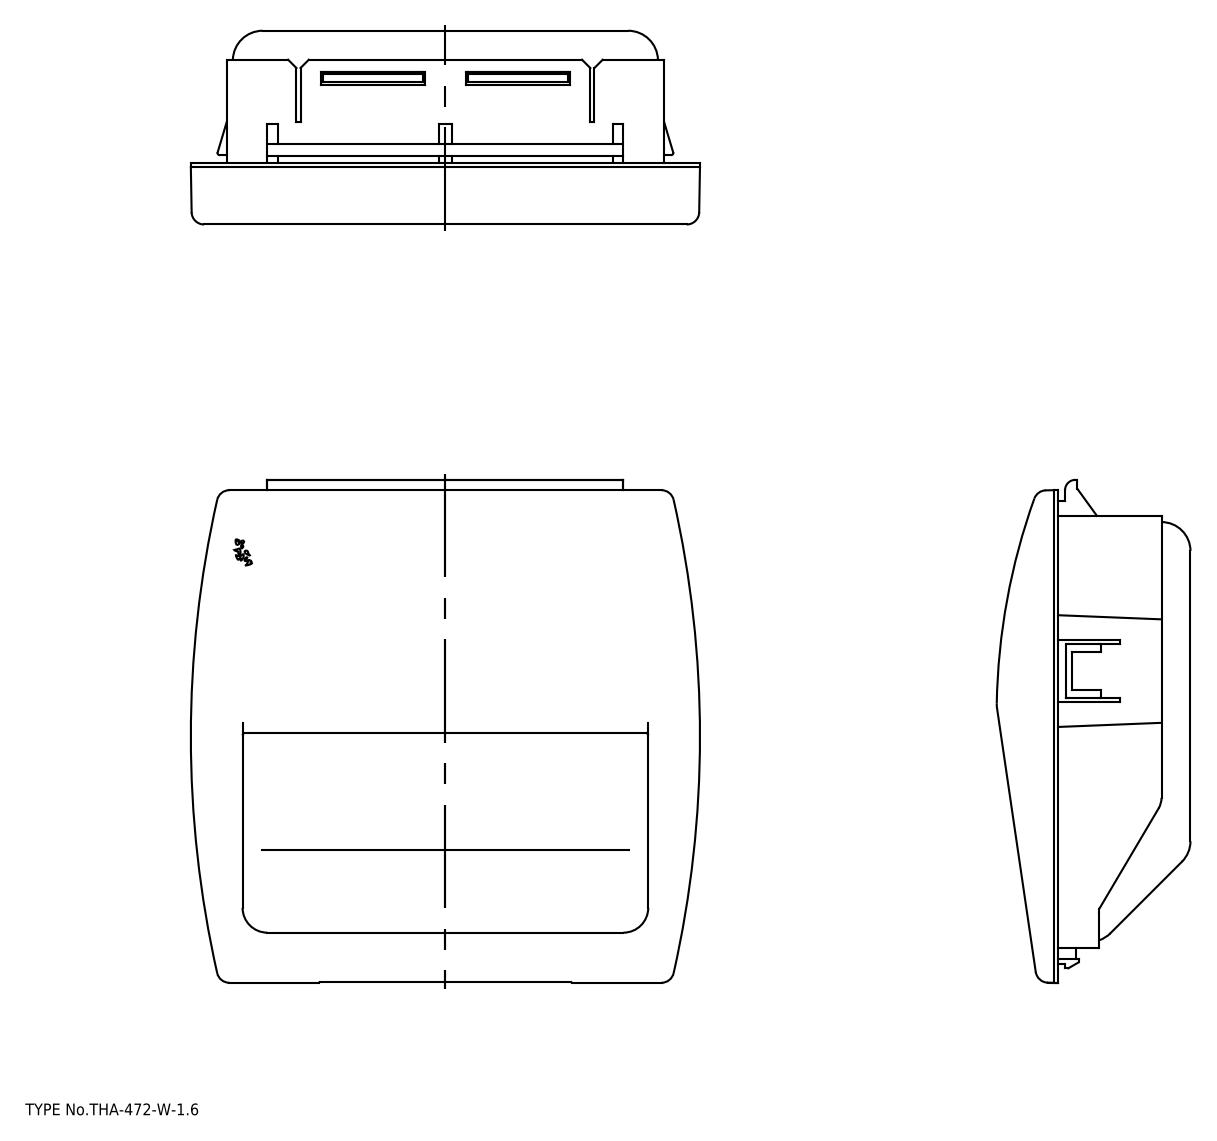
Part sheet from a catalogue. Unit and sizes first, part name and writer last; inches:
Units: inches
Overall size (bounding box): 4.843 × 4.783 × 1.843
Round holes (diameter × count): ⌀0.134 ×2
Partial cylindrical surfaces — rounded edges, fillets, slot ends (radius × count): R0.02 ×112, R0.039 ×23, R0.276 ×21, R0.197 ×14, R0.012 ×11, R0.335 ×8, R0.024 ×4, R0.118 ×4
Main face-to-face distances: 0.079, 4.102, 0.059, 0.138, 3.965, 4.043, 4.024, 1.26, 1.181, 3.886
Hole centre spacings: 2.047
Volume: 6.563 in³ · Surface area: 158.7 in²
Bodies: 3 solids, 703 faces (275 planar, 264 cylindrical, 164 other)
Part name (STEP PRODUCT): case; grip
STEP written by: spGate 19.8.4 (****-****-****-****) (AUTOMOTIVE_DESIGN)
